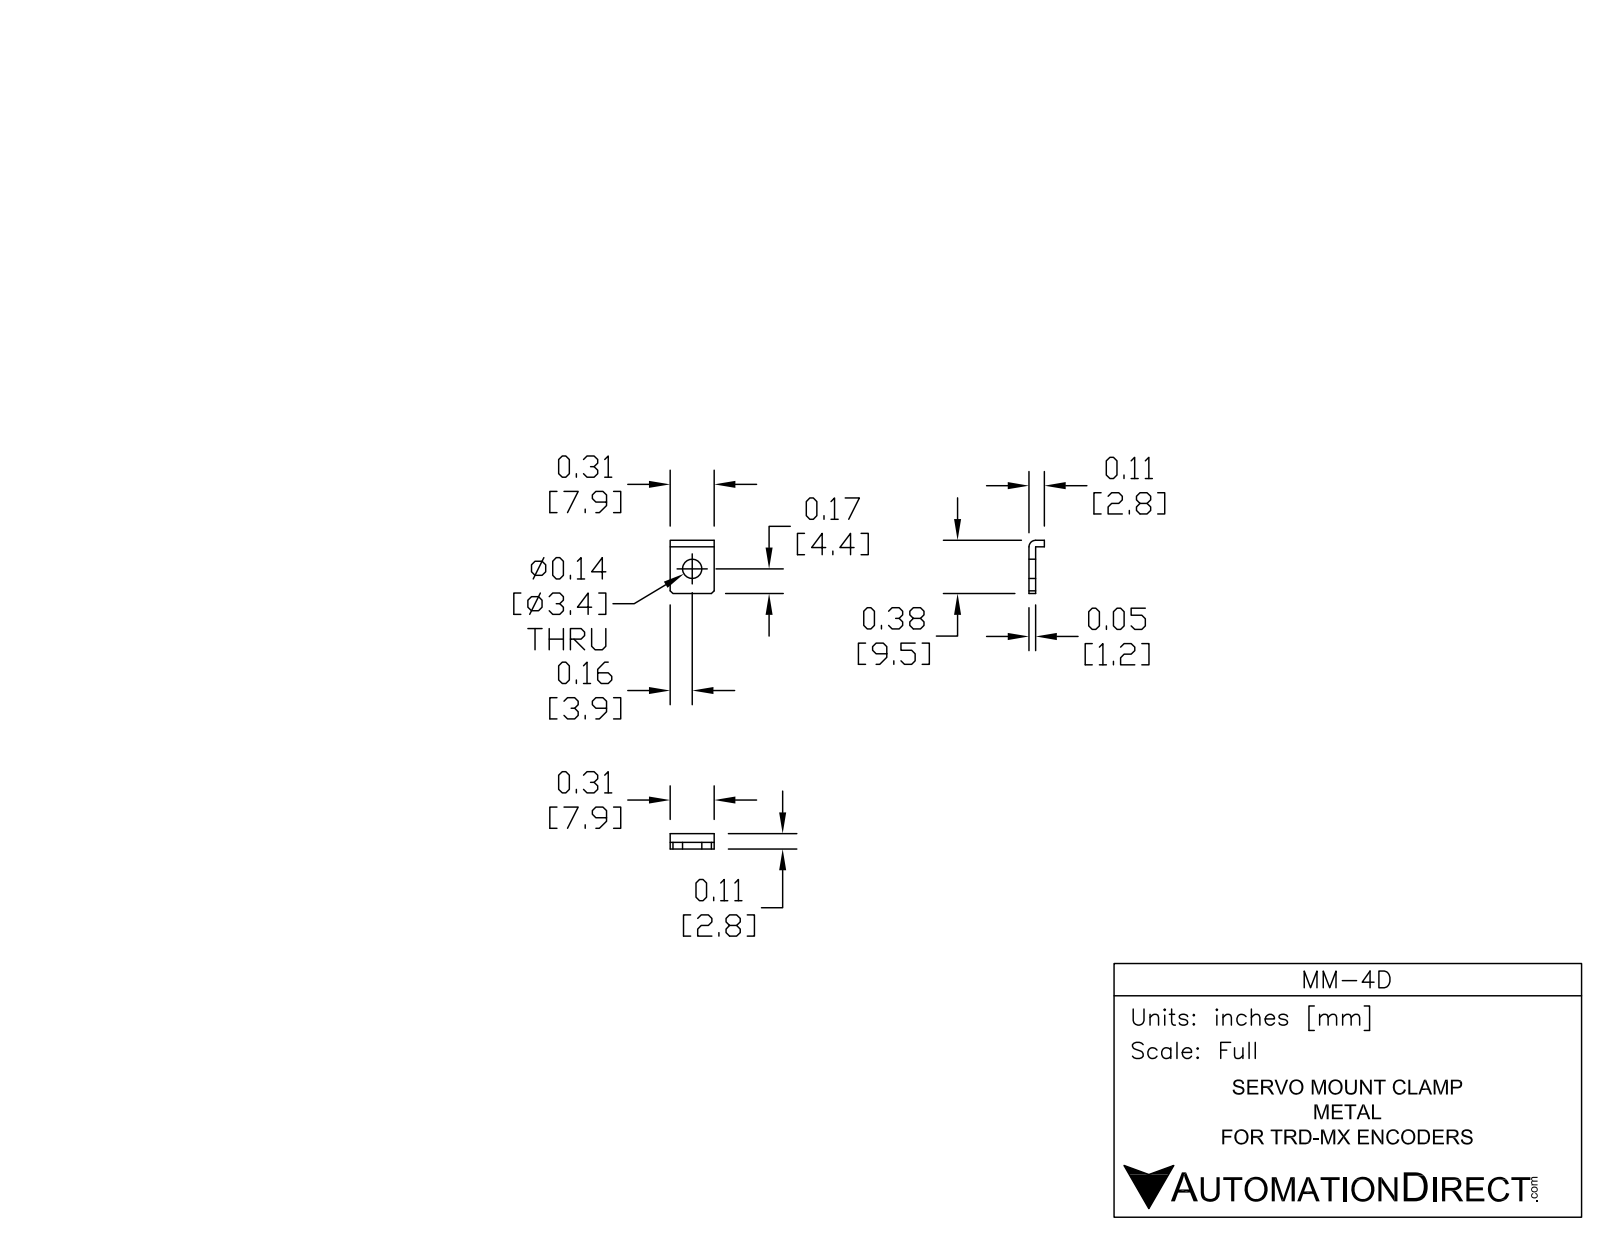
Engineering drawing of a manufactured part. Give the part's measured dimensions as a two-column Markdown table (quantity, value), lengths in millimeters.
| quantity | value |
| --- | --- |
| part name | KANAGU_MM4 |
| STEP written by | PRO/ENGINEER BY PARAMETRIC TECHNOLOGY CORPORATION, 2010020 (AUTOMOTIVE_DESIGN_CC2) |
| units | millimeters |
| bodies | 1 solid, 13 faces (10 planar, 3 cylindrical, 0 other) |
| overall size | 9.7 × 8 × 2.8 |
| volume | 94 mm³ |
| surface area | 215 mm² |
| round holes (diameter × count) | 3.5 × 1 |
| partial cylindrical surfaces (radius × count) | 1.2 × 1 |
| main face-to-face distances | 1.2, 8, 1.6, 2.8, 9.7, 8.5 |
